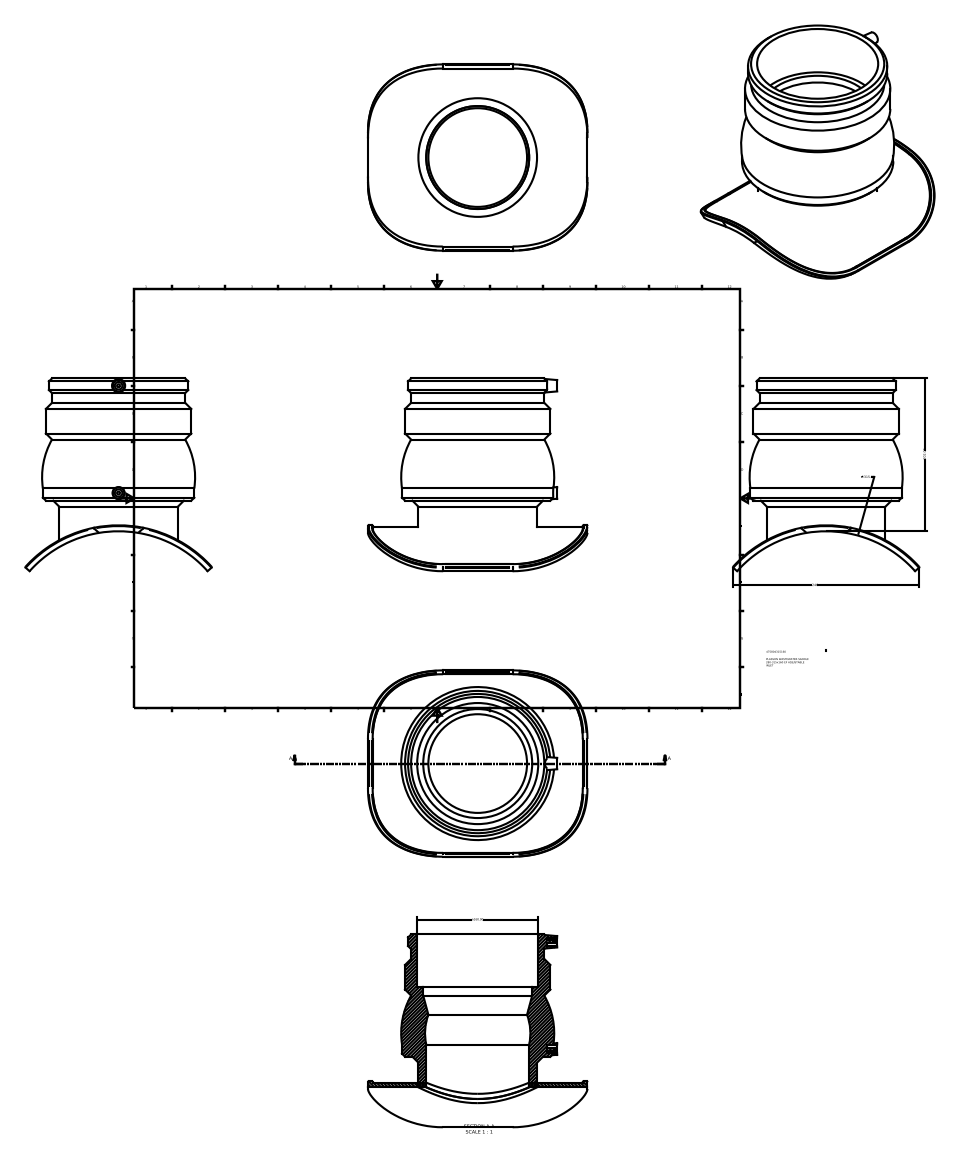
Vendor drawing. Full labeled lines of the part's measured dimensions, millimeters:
Part name (STEP PRODUCT): 475804315160
STEP written by: Autodesk Inventor 2015 (AUTOMOTIVE_DESIGN)
Units: millimetres
Bodies: 2 solids, 69 faces (17 planar, 29 cylindrical, 23 other)
Overall size (bounding box): 290 × 254.75 × 246.18
Volume: 2 464 000 mm³ · Surface area: 369 996 mm²
Round holes (diameter × count): ⌀10 ×2, ⌀136 ×1, ⌀144 ×1, ⌀160 ×1
Round bosses / shafts (diameter × count): ⌀4 ×2, ⌀200 ×1, ⌀192 ×1, ⌀184 ×1, ⌀176 ×1, ⌀156.8 ×1
Partial cylindrical surfaces — rounded edges, fillets, slot ends (radius × count): R0.99 ×4, R92.62 ×4, R98.8 ×4, R157.5 ×1, R163.68 ×1, R165.38 ×1
Main face-to-face distances: 161.6, 91.6, 70, 290, 250, 40, 6.18, 236, 14, 54
Hole centre spacings: 141.82
